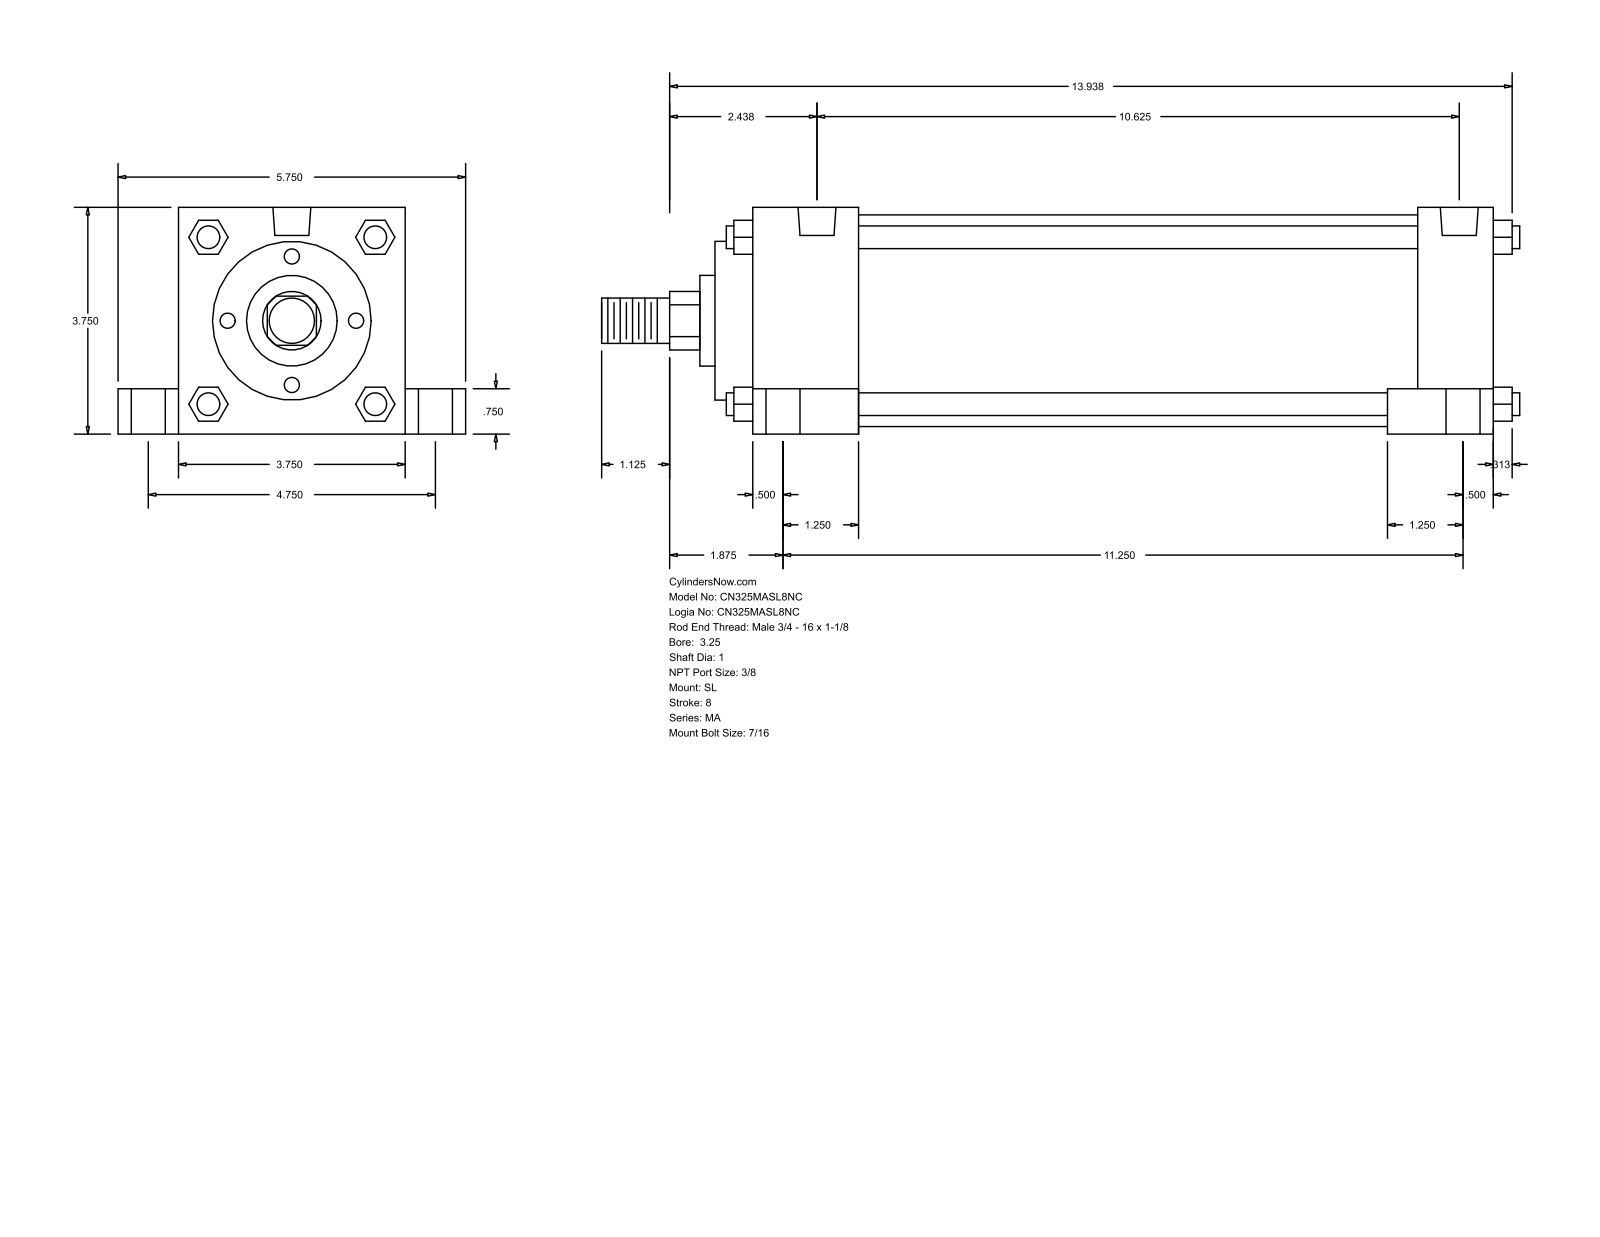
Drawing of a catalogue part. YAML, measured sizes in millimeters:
part_name: "MA_SL__0325_1"
step_written_by: "GSSL Pune (CONFIG_CONTROL_DESIGN)"
units: millimeters
bodies: {solids: 0, faces: 150, planar: 113, cylindrical: 37, other: 0}
overall_size: [385.76, 146.05, 95.25]
round_holes:
  - {diameter: 11.11, count: 4}
  - {diameter: 14.29, count: 4}
  - {diameter: 20.64, count: 4}
  - {diameter: 15.93, count: 2}
round_bosses_or_shafts:
  - {diameter: 9.53, count: 4}
  - {diameter: 88.9, count: 1}
  - {diameter: 66.67, count: 1}
  - {diameter: 38.1, count: 1}
  - {diameter: 25.4, count: 1}
  - {diameter: 19.05, count: 1}
partial_cylinders:
  - {radius: 12.29, count: 1}
face_to_face_distances: [95.24, 311.15, 15.87, 25.41, 120.65, 327.02, 19.05, 279.4, 31.75, 44.46]
hole_center_spacings: [60.35, 60.66, 62, 63.27, 120.66, 260.35, 273.45, 278.09]
